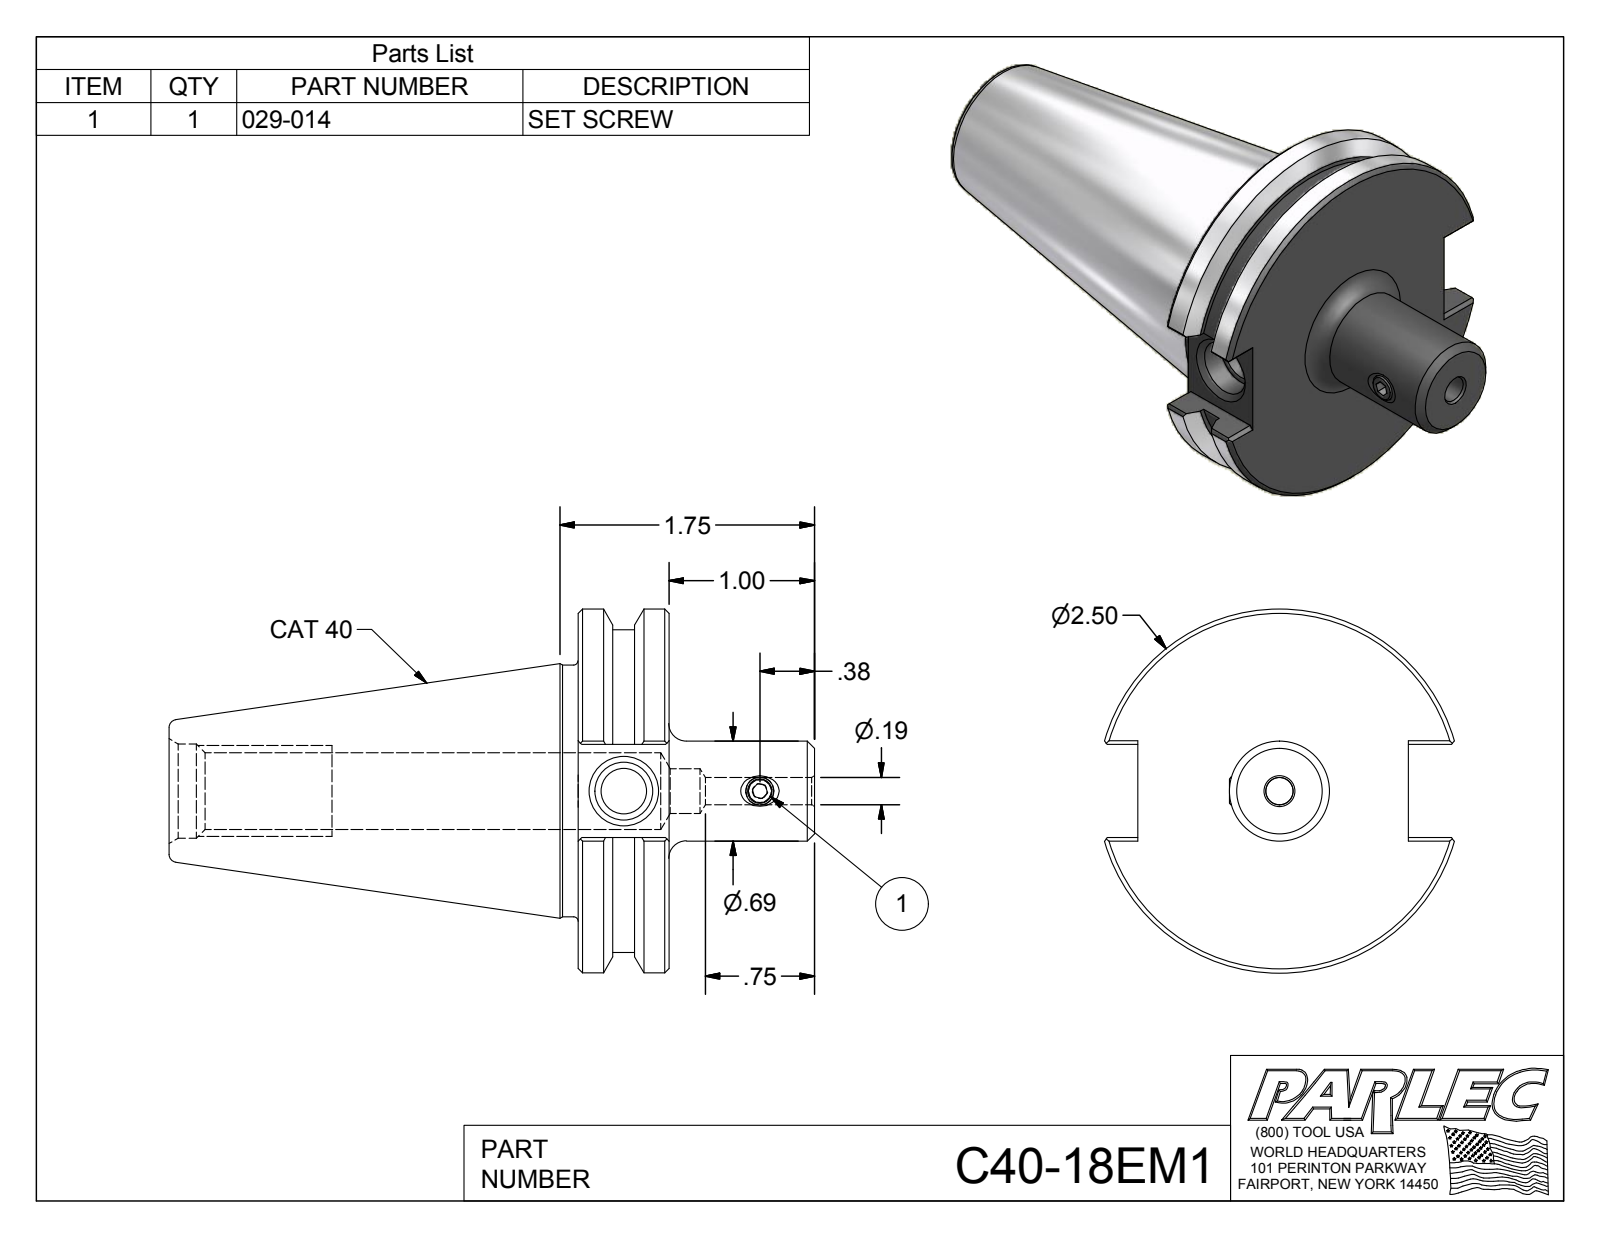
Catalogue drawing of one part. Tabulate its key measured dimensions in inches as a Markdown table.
| quantity | value |
| --- | --- |
| part name | C40-18EM1; C40-18EM1-1; 029-014 |
| STEP written by | Autodesk Inventor 2012 (AUTOMOTIVE_DESIGN) |
| units | inches |
| bodies | 2 solids, 81 faces (41 planar, 16 cylindrical, 24 other) |
| overall size | 4.438 × 2.5 × 2.403 |
| volume | 6.465 in³ |
| surface area | 34.55 in² |
| round holes (diameter × count) | 0.159 × 1, 0.187 × 1, 0.307 × 1, 0.315 × 1, 0.396 × 1, 0.527 × 1, 0.648 × 1 |
| round bosses / shafts (diameter × count) | 2.5 × 1, 2.219 × 1, 1.73 × 1, 0.687 × 1, 0.19 × 1 |
| main face-to-face distances | 0.625, 0.64, 1.625, 1, 1.86, 2.813, 3.437, 4.437, 3.201, 0.389 |
| hole center spacings | 0.935 |
